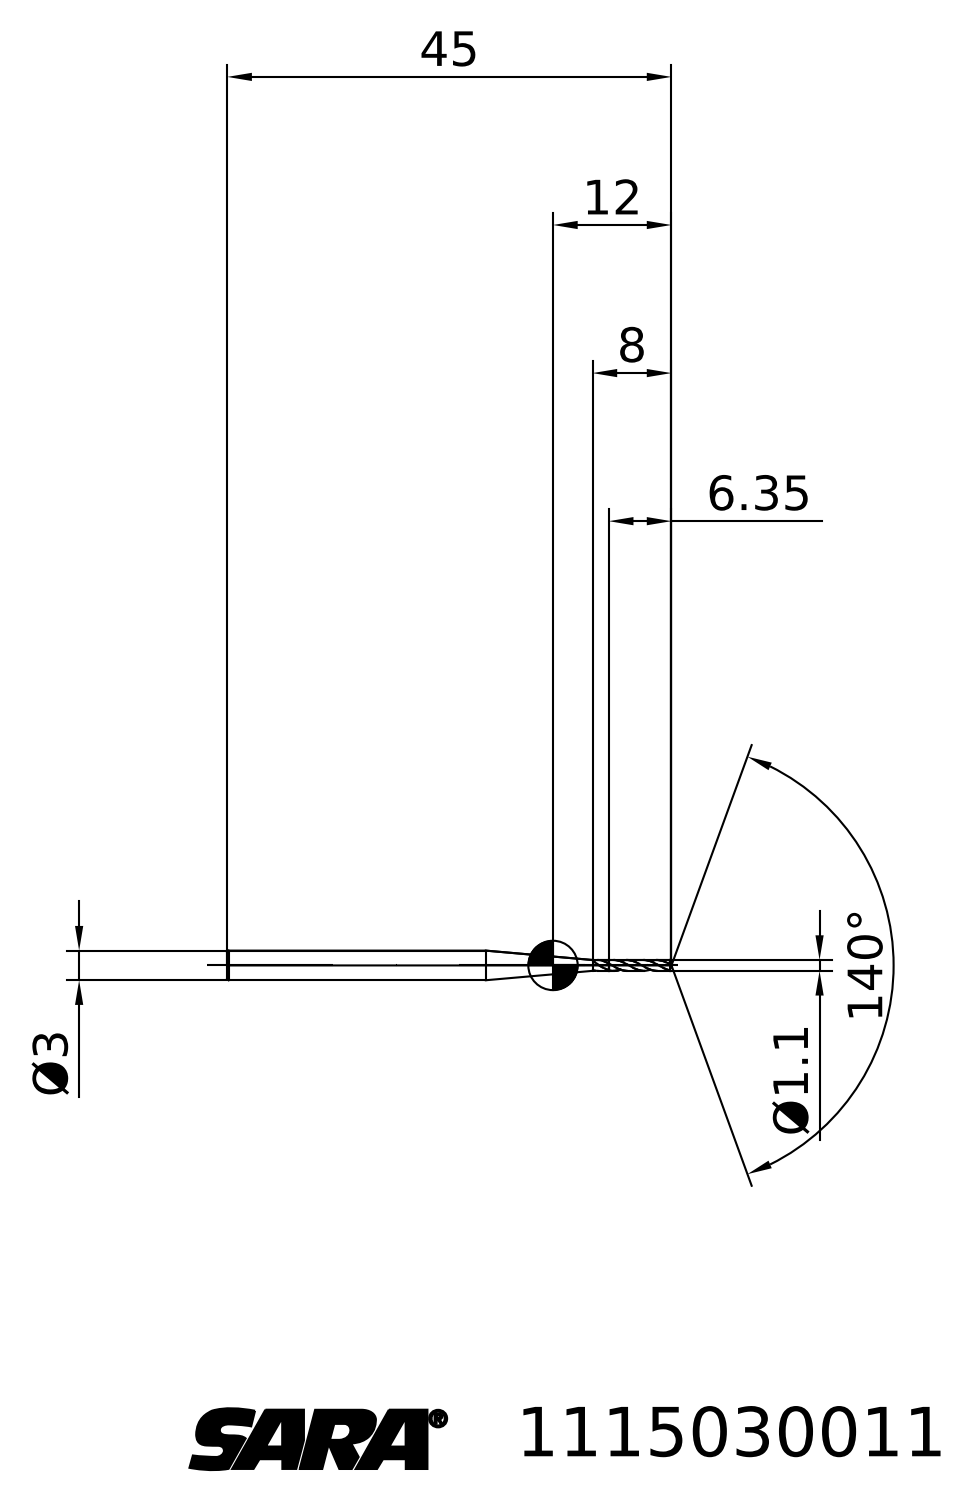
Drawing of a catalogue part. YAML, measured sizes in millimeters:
step_written_by: "TDM (AUTOMOTIVE_DESIGN)"
units: millimeters
bodies: {solids: 2, faces: 27, planar: 3, cylindrical: 0, other: 24}
overall_size: [45, 3, 3]
volume: 228
surface_area: 354
face_to_face_distances: [38.65]
